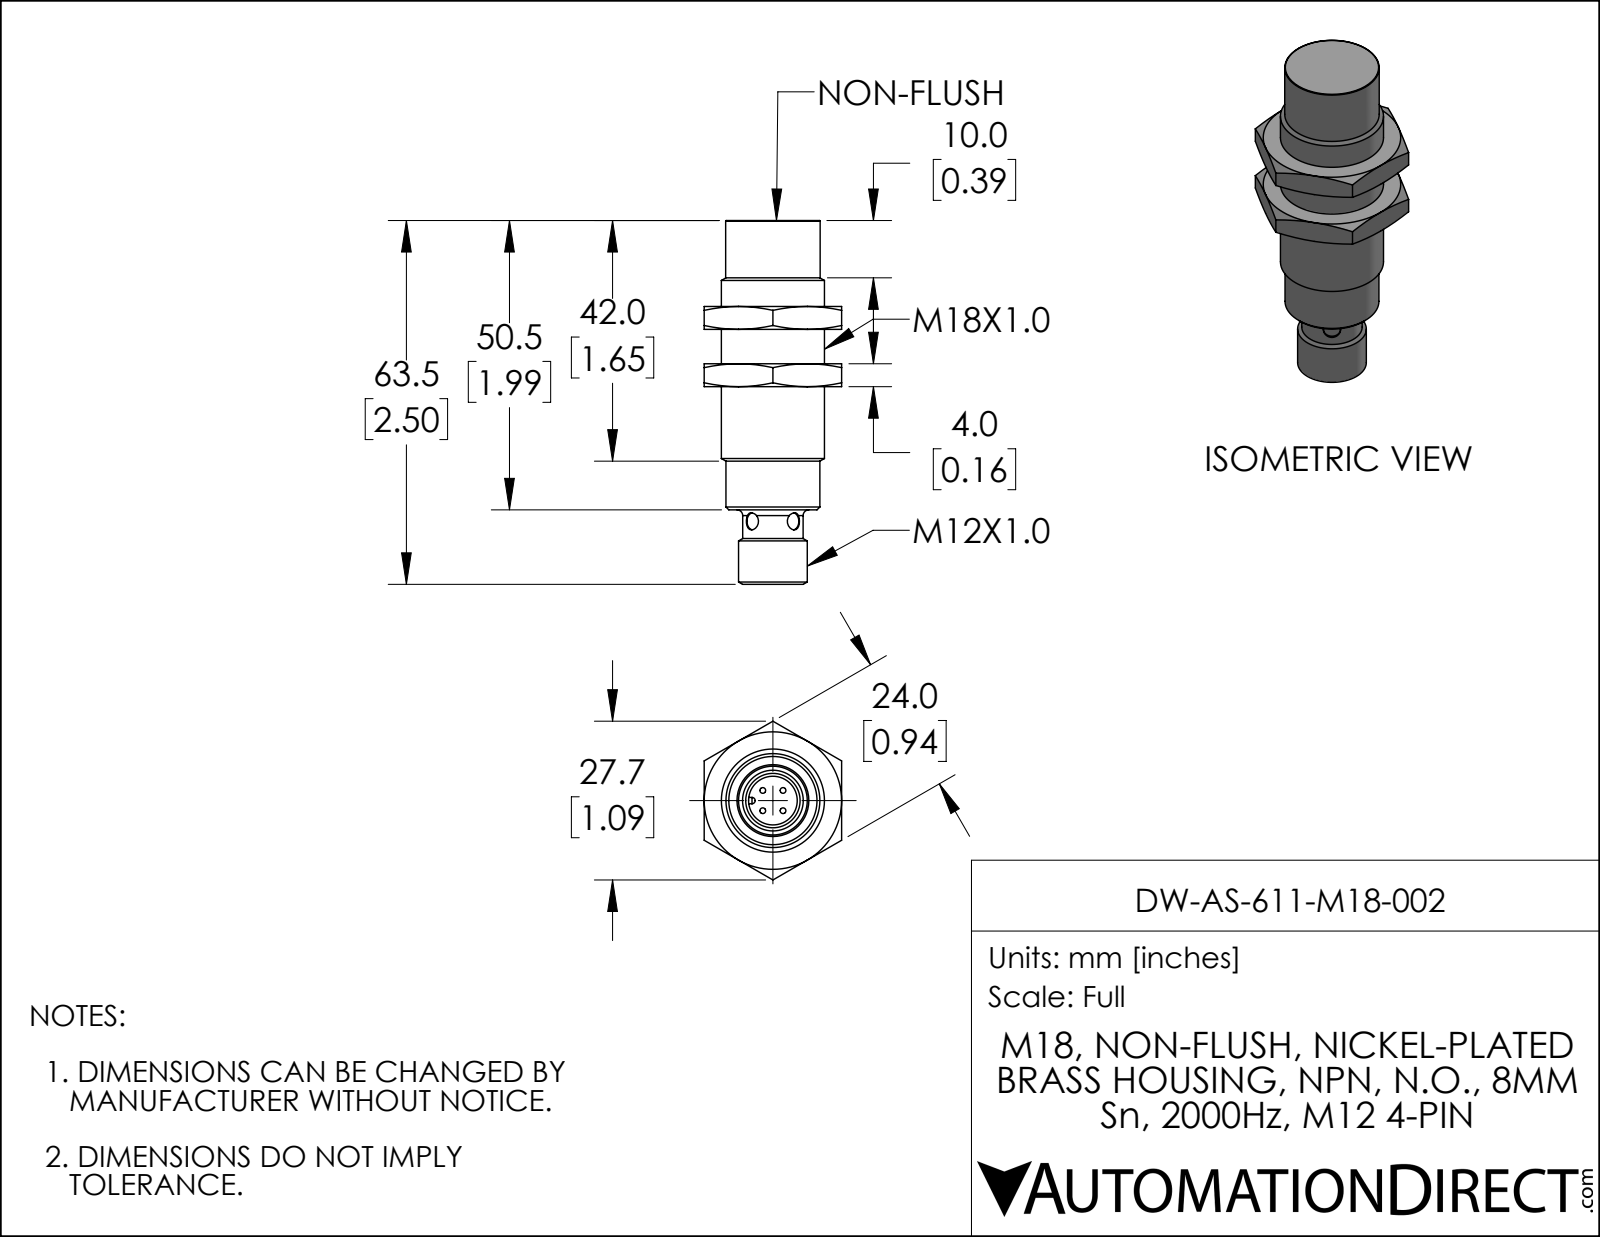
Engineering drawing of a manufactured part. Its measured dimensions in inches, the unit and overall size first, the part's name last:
Units: inches
Overall size (bounding box): 2.5 × 1.091 × 0.945
Round holes (diameter × count): ⌀0.118 ×2, ⌀0.335 ×1
Round bosses / shafts (diameter × count): ⌀0.039 ×4, ⌀0.709 ×1, ⌀0.65 ×1, ⌀0.646 ×1, ⌀0.472 ×1, ⌀0.415 ×1
Partial cylindrical surfaces — rounded edges, fillets, slot ends (radius × count): R0.022 ×2
Main face-to-face distances: 0.394, 0.157, 0.945, 0.591, 0.748, 0.984, 1.142, 0.551, 0.236, 1.988
Volume: 0.905 in³ · Surface area: 8.005 in²
Bodies: 1 solid, 82 faces (27 planar, 18 cylindrical, 37 other)
Part name (STEP PRODUCT): DW-AS-611-M18-002
STEP written by: SolidWorks 2019 (AUTOMOTIVE_DESIGN)
